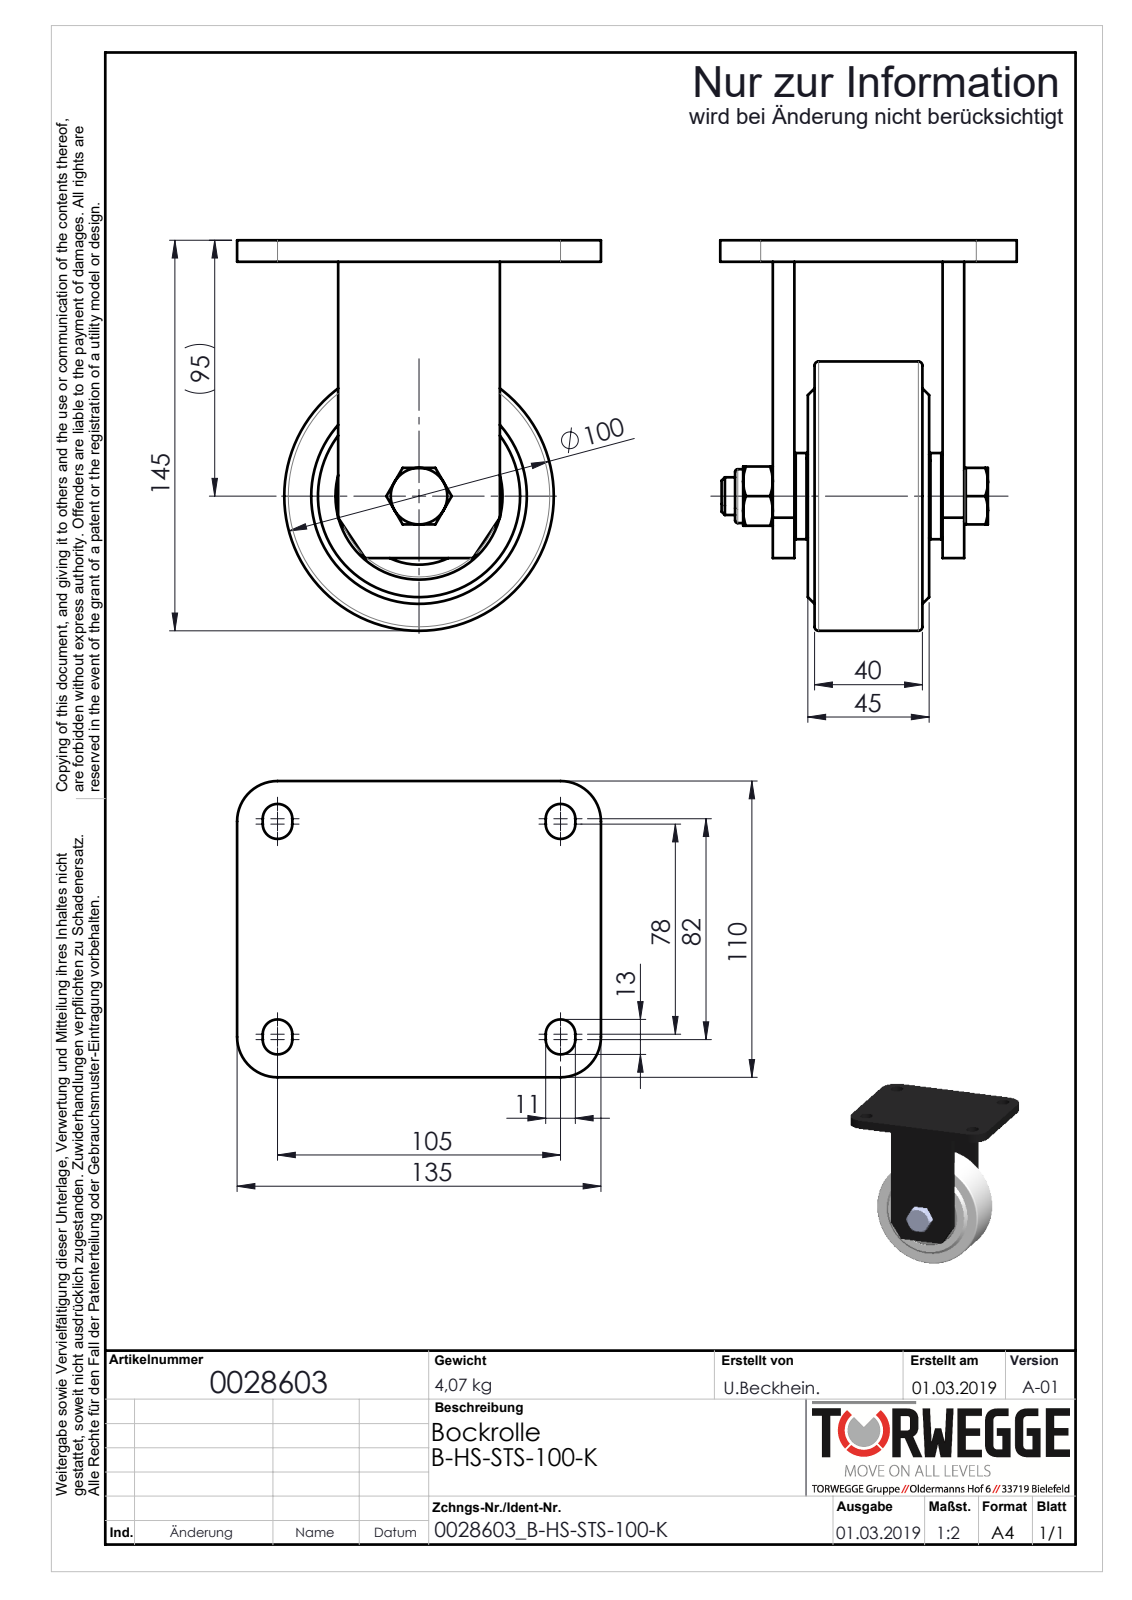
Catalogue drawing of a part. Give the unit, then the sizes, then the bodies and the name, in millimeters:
Units: millimetres
Overall size (bounding box): 145 × 135 × 110
Round holes (diameter × count): ⌀11.84 ×1, ⌀14 ×1, ⌀14.3 ×1, ⌀25 ×1, ⌀50.9 ×1, ⌀55 ×1, ⌀62 ×1
Round bosses / shafts (diameter × count): ⌀100 ×1, ⌀36.1 ×1, ⌀32 ×1, ⌀20 ×1
Partial cylindrical surfaces — rounded edges, fillets, slot ends (radius × count): R5.5 ×8, R15 ×4
Main face-to-face distances: 8, 63, 55, 71, 5, 13, 58, 50, 15.5, 55.5
Bodies: 0 solids, 202 faces (64 planar, 58 cylindrical, 80 other)
Part name (STEP PRODUCT): 0028603_B-HS-STS-100-K_(A-01)
STEP written by: SolidWorks 2018 (AUTOMOTIVE_DESIGN)
